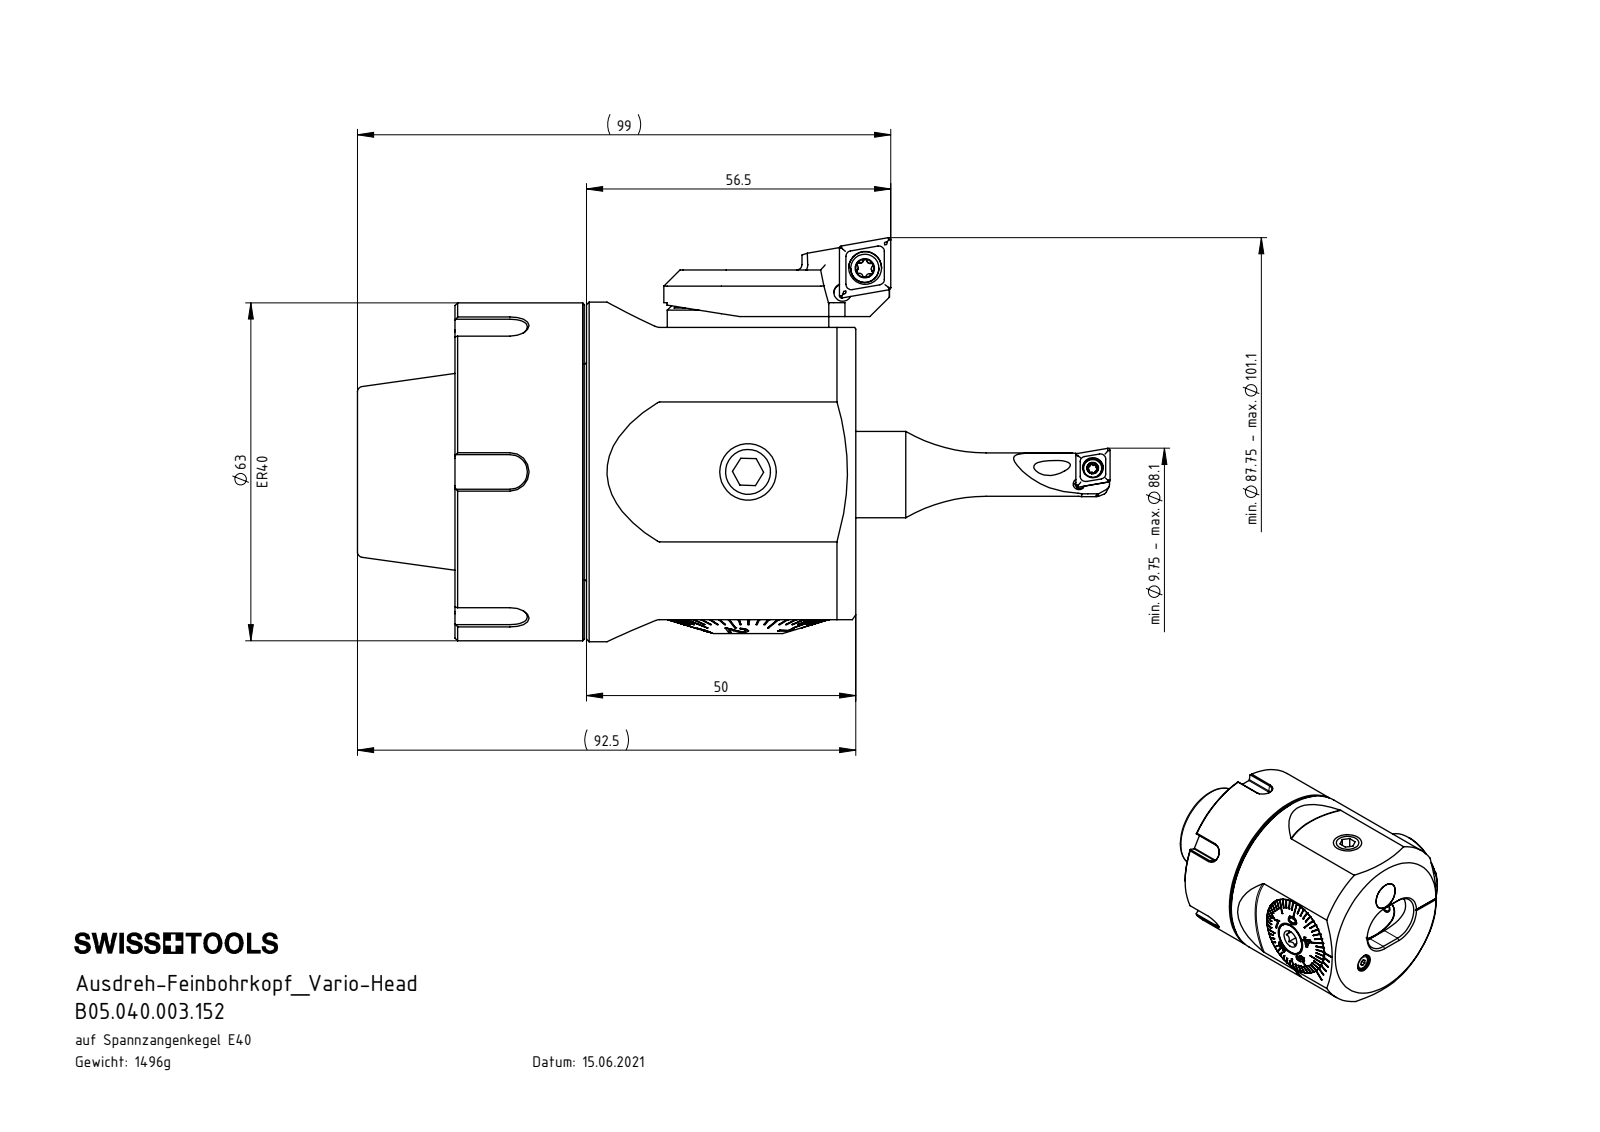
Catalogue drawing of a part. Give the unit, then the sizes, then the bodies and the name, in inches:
Units: inches
Overall size (bounding box): 3.642 × 2.55 × 2.48
Round holes (diameter × count): ⌀0.13 ×2, ⌀0.236 ×2, ⌀0.335 ×2, ⌀0.039 ×1, ⌀0.098 ×1, ⌀0.165 ×1, ⌀0.315 ×1, ⌀0.394 ×1, ⌀0.463 ×1, ⌀0.472 ×1, ⌀0.488 ×1, ⌀0.551 ×1
Round bosses / shafts (diameter × count): ⌀0.394 ×2, ⌀2.48 ×1, ⌀2.469 ×1, ⌀1.575 ×1, ⌀1.476 ×1, ⌀1.181 ×1, ⌀1.18 ×1, ⌀1.177 ×1
Partial cylindrical surfaces — rounded edges, fillets, slot ends (radius × count): R0.012 ×12, R0.02 ×4, R0.055 ×4, R0.075 ×4, R0.126 ×3, R0.335 ×3, R0.059 ×2, R0.039 ×1
Main face-to-face distances: 1.969, 0.016, 1.984, 0.945, 0.961, 2.929, 2.272, 0.106, 0.11, 0.098
Hole centre spacings: 0.065, 0.413, 0.571, 0.574, 0.604, 0.654, 1.073
Volume: 11.66 in³ · Surface area: 92.84 in²
Bodies: 16 solids, 843 faces (374 planar, 150 cylindrical, 319 other)
Part name (STEP PRODUCT): DIN 3771 - 25x1.5; AV6-BG2.014.011_B_Abgedreht; E40-AV6.AA3.062_B; ISO 4026 - M10 x 10_PreviewCfg (+8 more)
STEP written by: SolidWorks 2022 (CONFIG_CONTROL_DESIGN)
